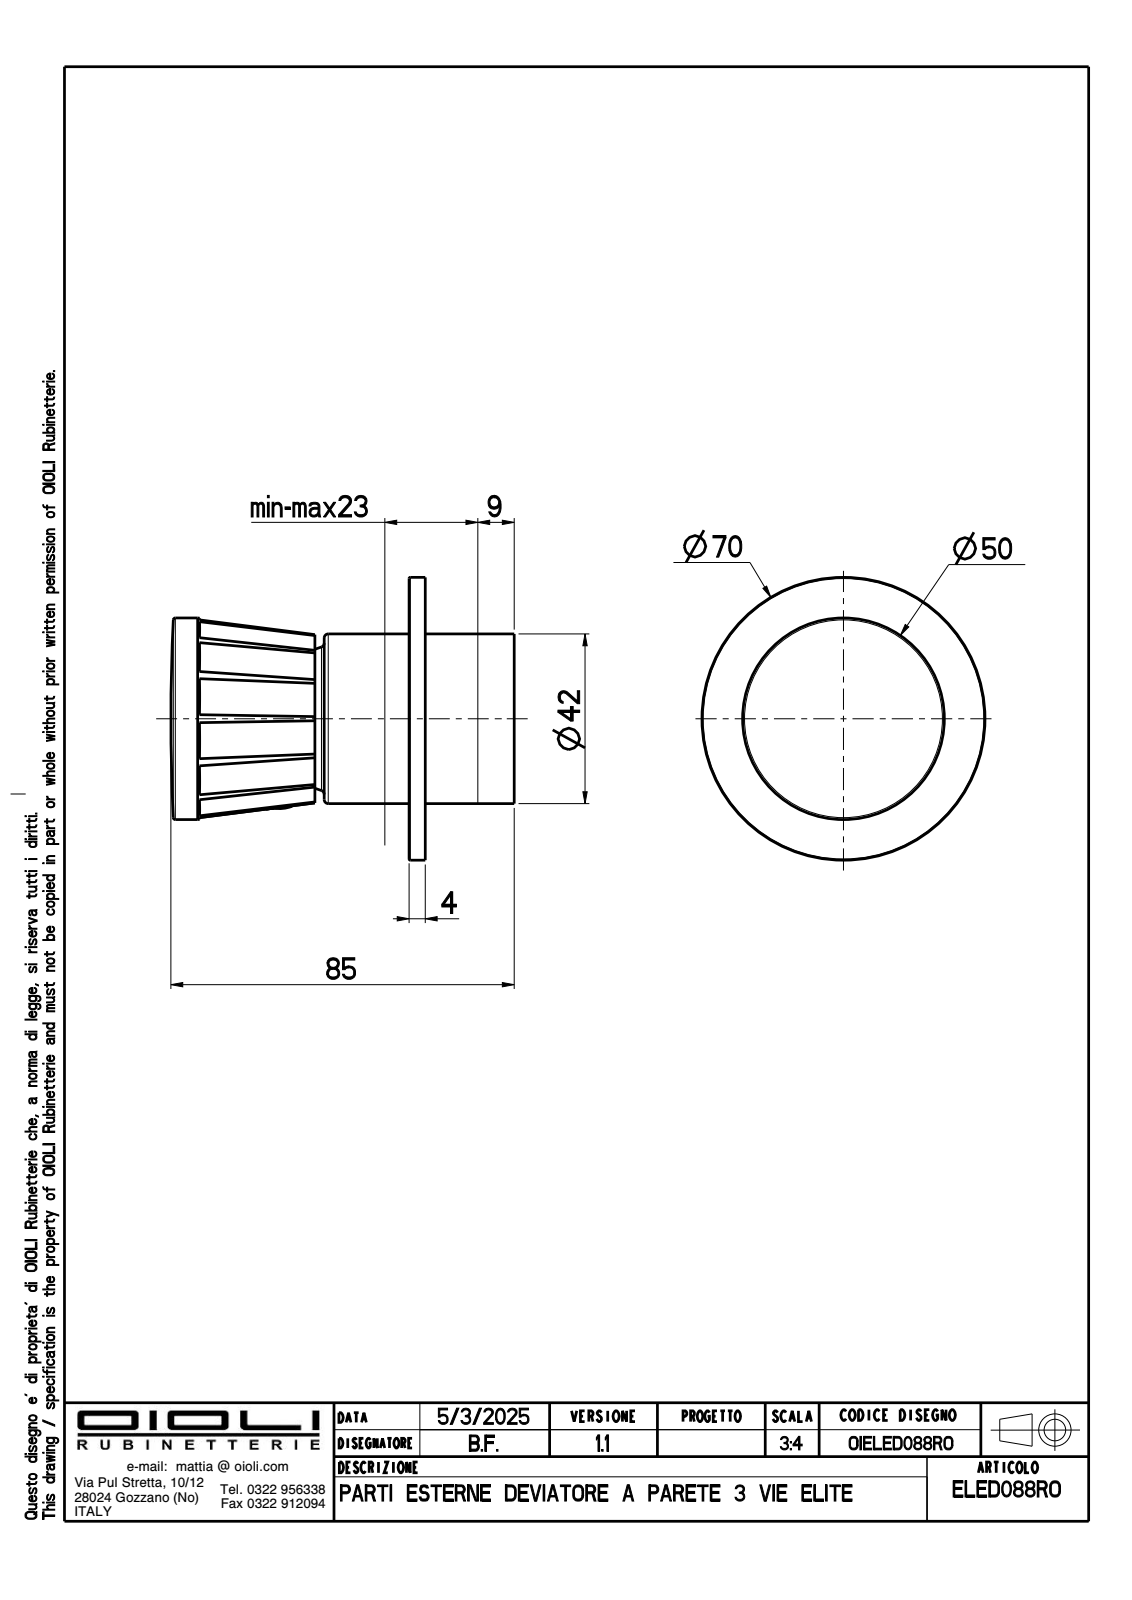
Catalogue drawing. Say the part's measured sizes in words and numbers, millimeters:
The part is named "OIBR00949; OIBR00242; OIOR00091; OIBR00948 (+2 more)". Its 3-D file was written by "CREO PARAMETRIC BY PTC INC, 2024493 (CONFIG_CONTROL_DESIGN)". It is 5 solids with 157 faces: 61 planar, 48 cylindrical and 48 other. Overall it measures 84.92 by 70 by 70 millimeters. Its volume is 44 157 cubic millimeters and its surface area 37 021 square millimeters. Round holes: 1 of diameter 4, 1 of diameter 4.2, 1 of diameter 5.3, 1 of diameter 6.5, 1 of diameter 9.5, 1 of diameter 30, 1 of diameter 39.5, 1 of diameter 40, 1 of diameter 42.6, 1 of diameter 45.5. Round bosses or shafts: 1 of diameter 70, 1 of diameter 49.9, 1 of diameter 42, 1 of diameter 16.5, 1 of diameter 5. Partial cylindrical surfaces (rounded edges, fillets, slot ends): 10 of radius 0.1, 2 of radius 6.8. The main face-to-face distances are 4, 59.8, 55.8, 13, 17, 42.8, 22, 25, 1, 0.9.
